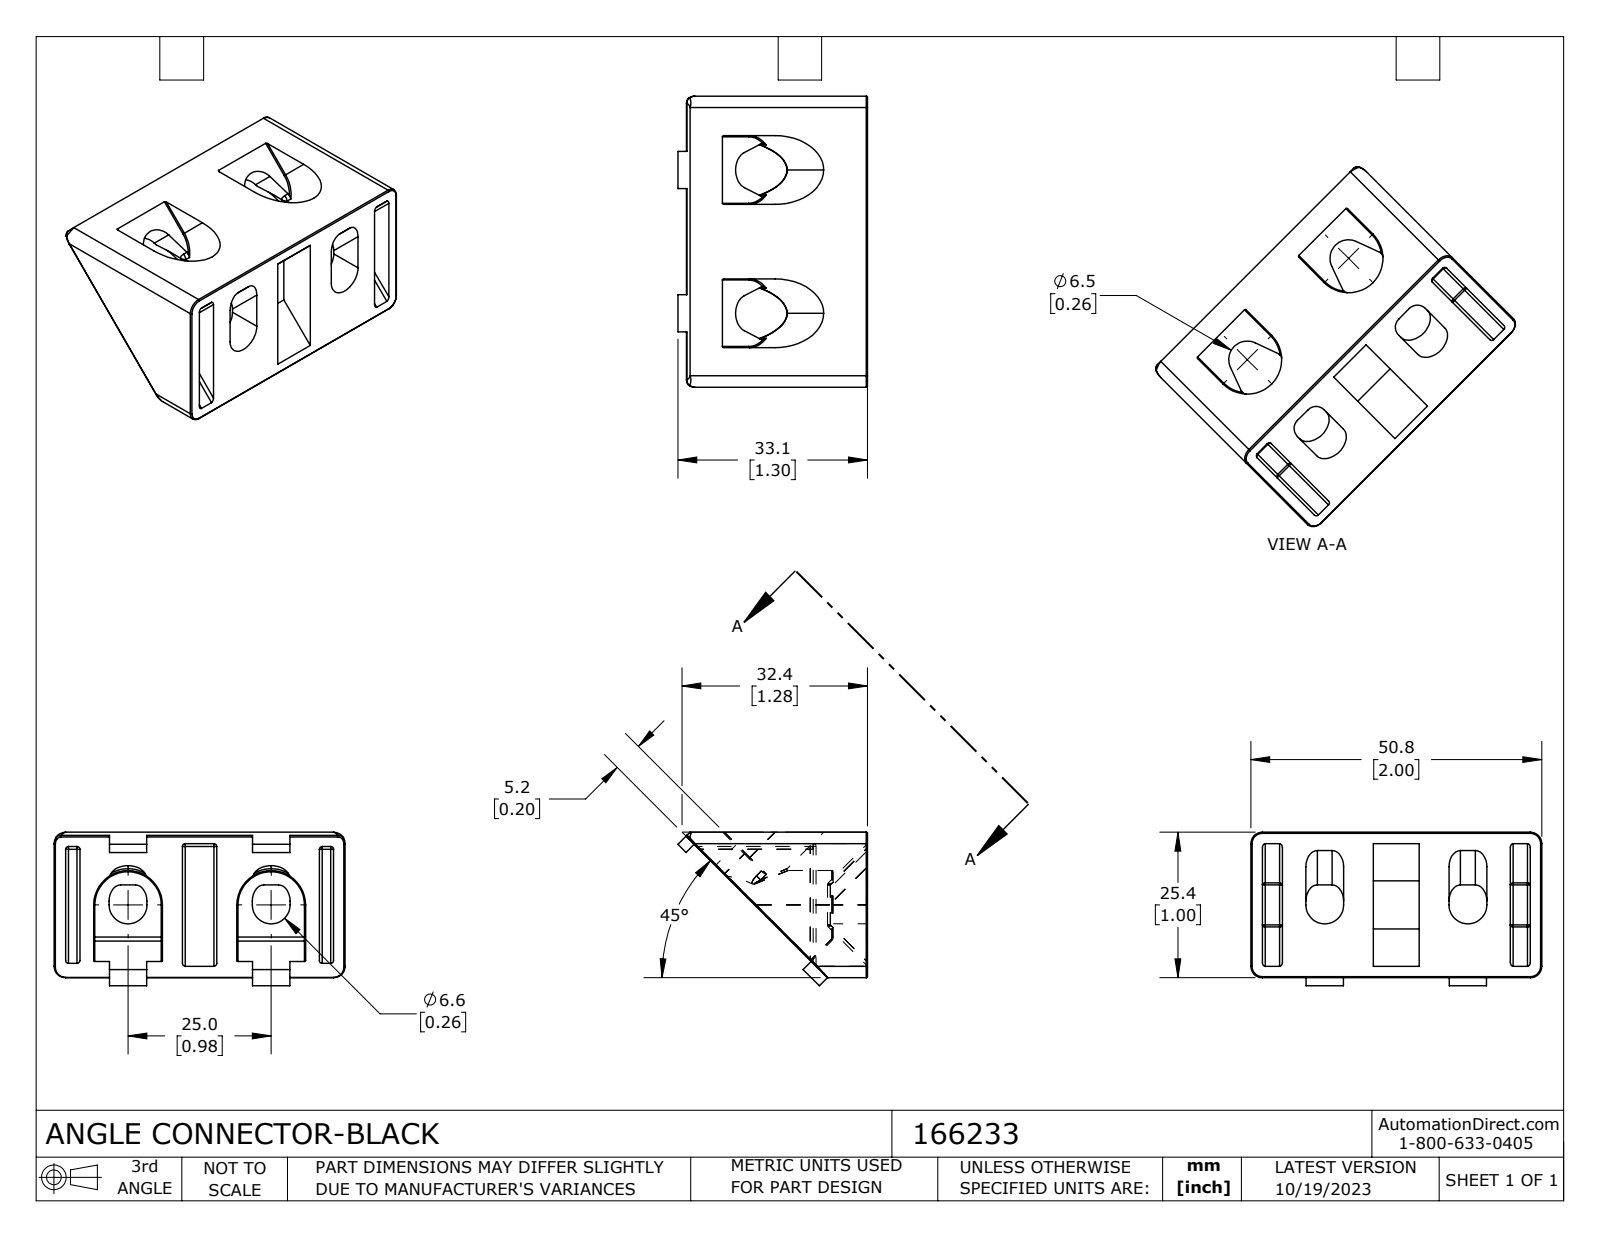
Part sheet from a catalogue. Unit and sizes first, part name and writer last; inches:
Units: inches
Overall size (bounding box): 2 × 1.567 × 0.978
Partial cylindrical surfaces — rounded edges, fillets, slot ends (radius × count): R0.02 ×28, R0.008 ×20, R0.079 ×8, R0.039 ×5, R0.236 ×4, R0.128 ×2, R0.13 ×2
Main face-to-face distances: 0.079, 0.098, 1.039, 0.665, 1.921, 0.941, 0.138, 0.882, 1.118, 0.803
Volume: 0.941 in³ · Surface area: 14.41 in²
Bodies: 1 solid, 199 faces (74 planar, 81 cylindrical, 44 other)
Part name (STEP PRODUCT): 166233
STEP written by: SolidWorks 2023 (CONFIG_CONTROL_DESIGN)
